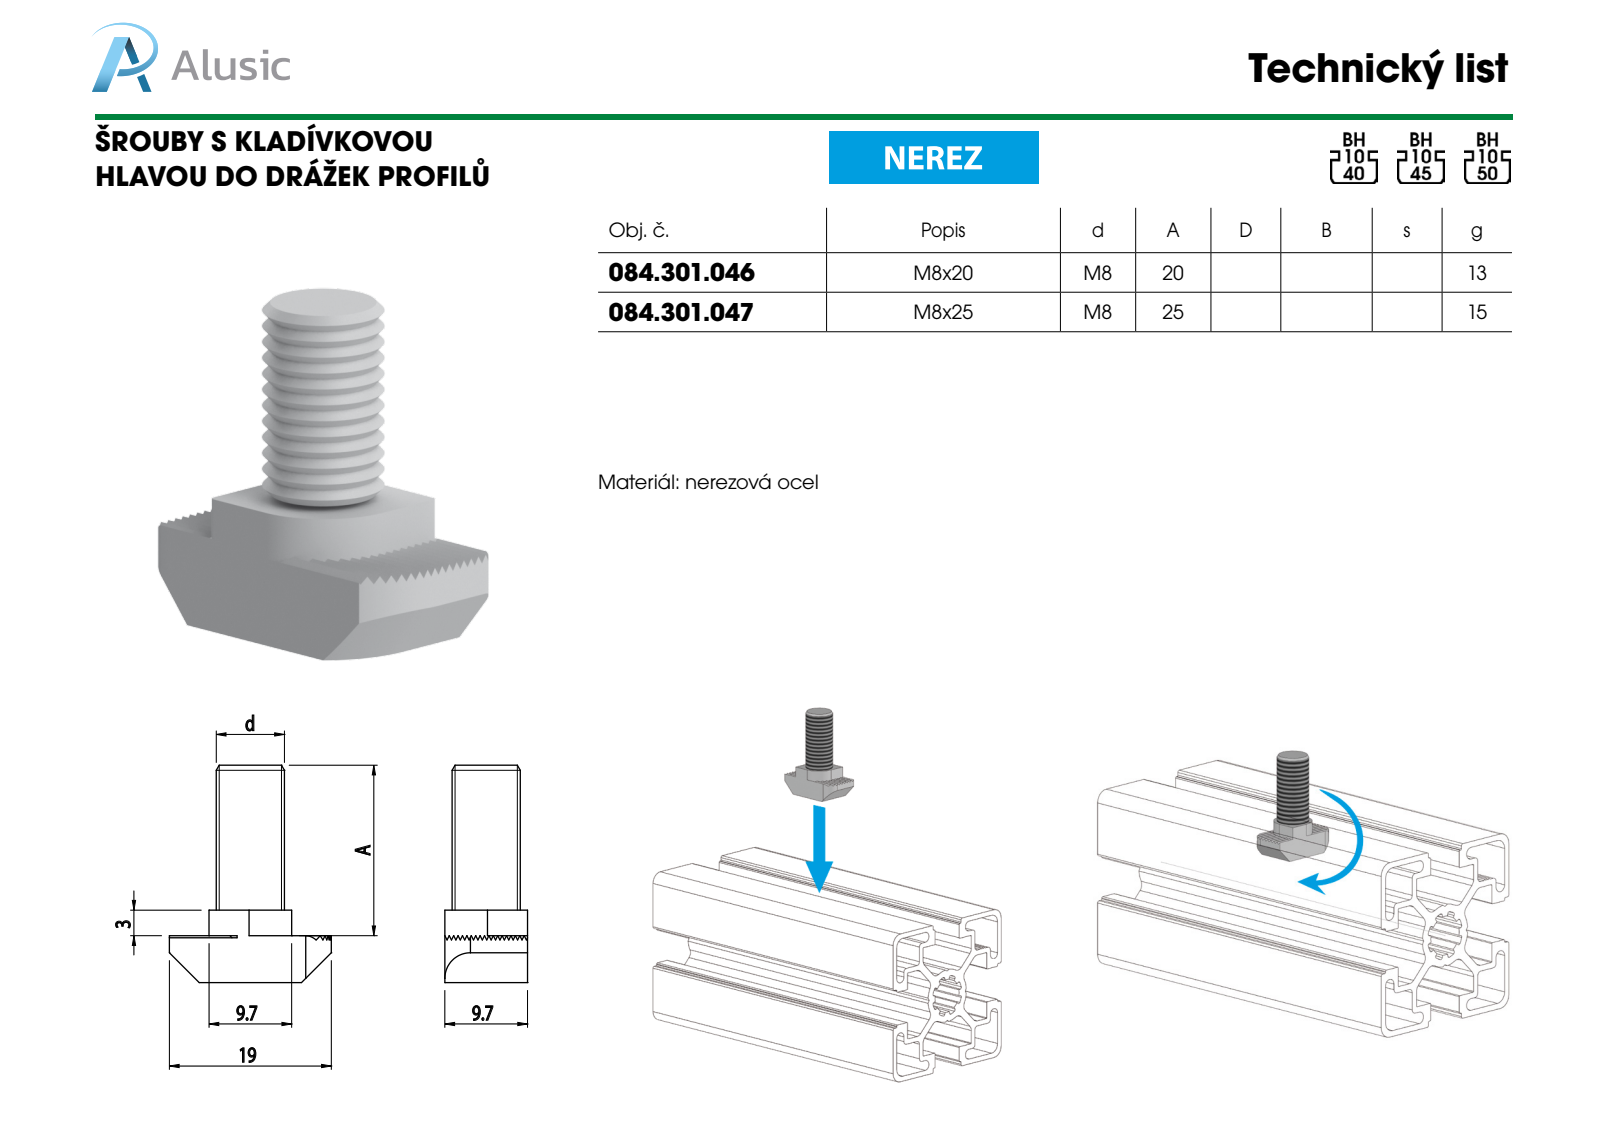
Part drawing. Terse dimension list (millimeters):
name: 084.301.046
written by: SolidWorks 2016 (CONFIG_CONTROL_DESIGN)
unit: mm
bodies: 1 solid, 137 faces (92 planar, 41 cylindrical, 4 other)
size: 25 × 19 × 9.7
volume: 1 801 mm³; area: 1 405 mm²
bosses: 1× ⌀8
rounds: 2× R0.3, 2× R5, 1× R4.85
face distances: 0.35, 0.7, 1.05, 9.7, 1.4, 1.75, 2.1, 2.45, 2.8, 3.15
